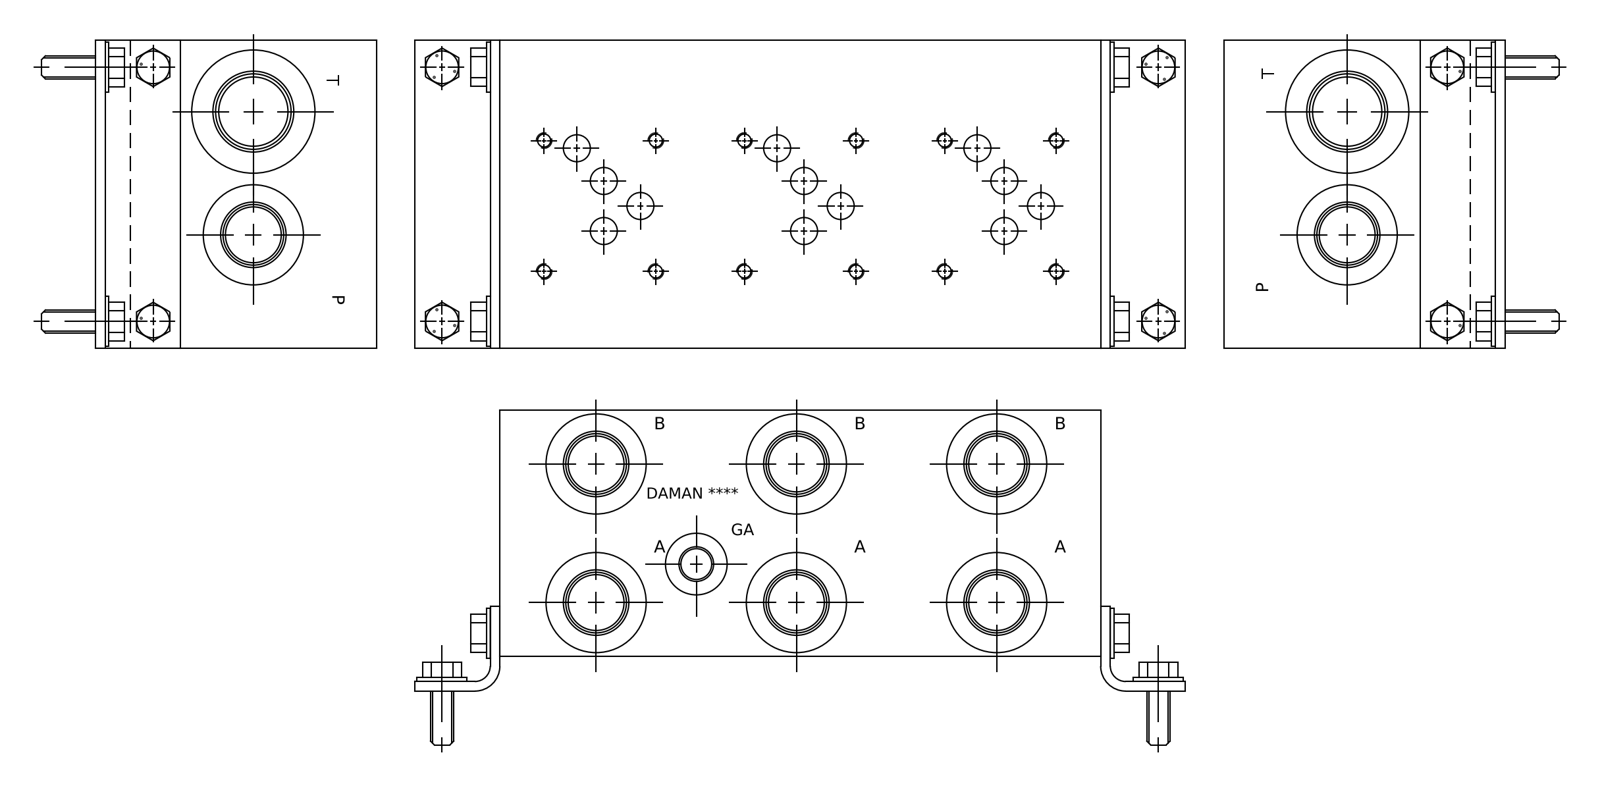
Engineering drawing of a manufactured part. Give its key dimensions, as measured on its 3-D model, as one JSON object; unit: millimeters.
{"part_name": "Part_AD05HP033S_3D", "step_written_by": "Autodesk Inventor 2019 (AUTOMOTIVE_DESIGN)", "units": "millimeters", "bodies": {"solids": 1, "faces": 762, "planar": 401, "cylindrical": 100, "other": 261}, "overall_size": [247.65, 127, 101.6], "volume_mm3": 2968000, "surface_area_mm2": 177751, "round_holes": [[5.11, 12], [6.35, 12], [11.13, 10], [23.01, 7], [24.92, 7], [27.43, 7], [42.04, 7], [27, 6], [7.92, 2], [9.53, 2], [11.11, 2], [26.99, 2]], "face_to_face_distances": [101.6, 127, 247.65, 0.79, 126.21, 246.86, 246.07, 19.05, 19.84, 107.16], "hole_center_spacings": [82.55, 98.63, 165.1, 46.05, 70.95, 53.98, 18.27, 29.74]}
